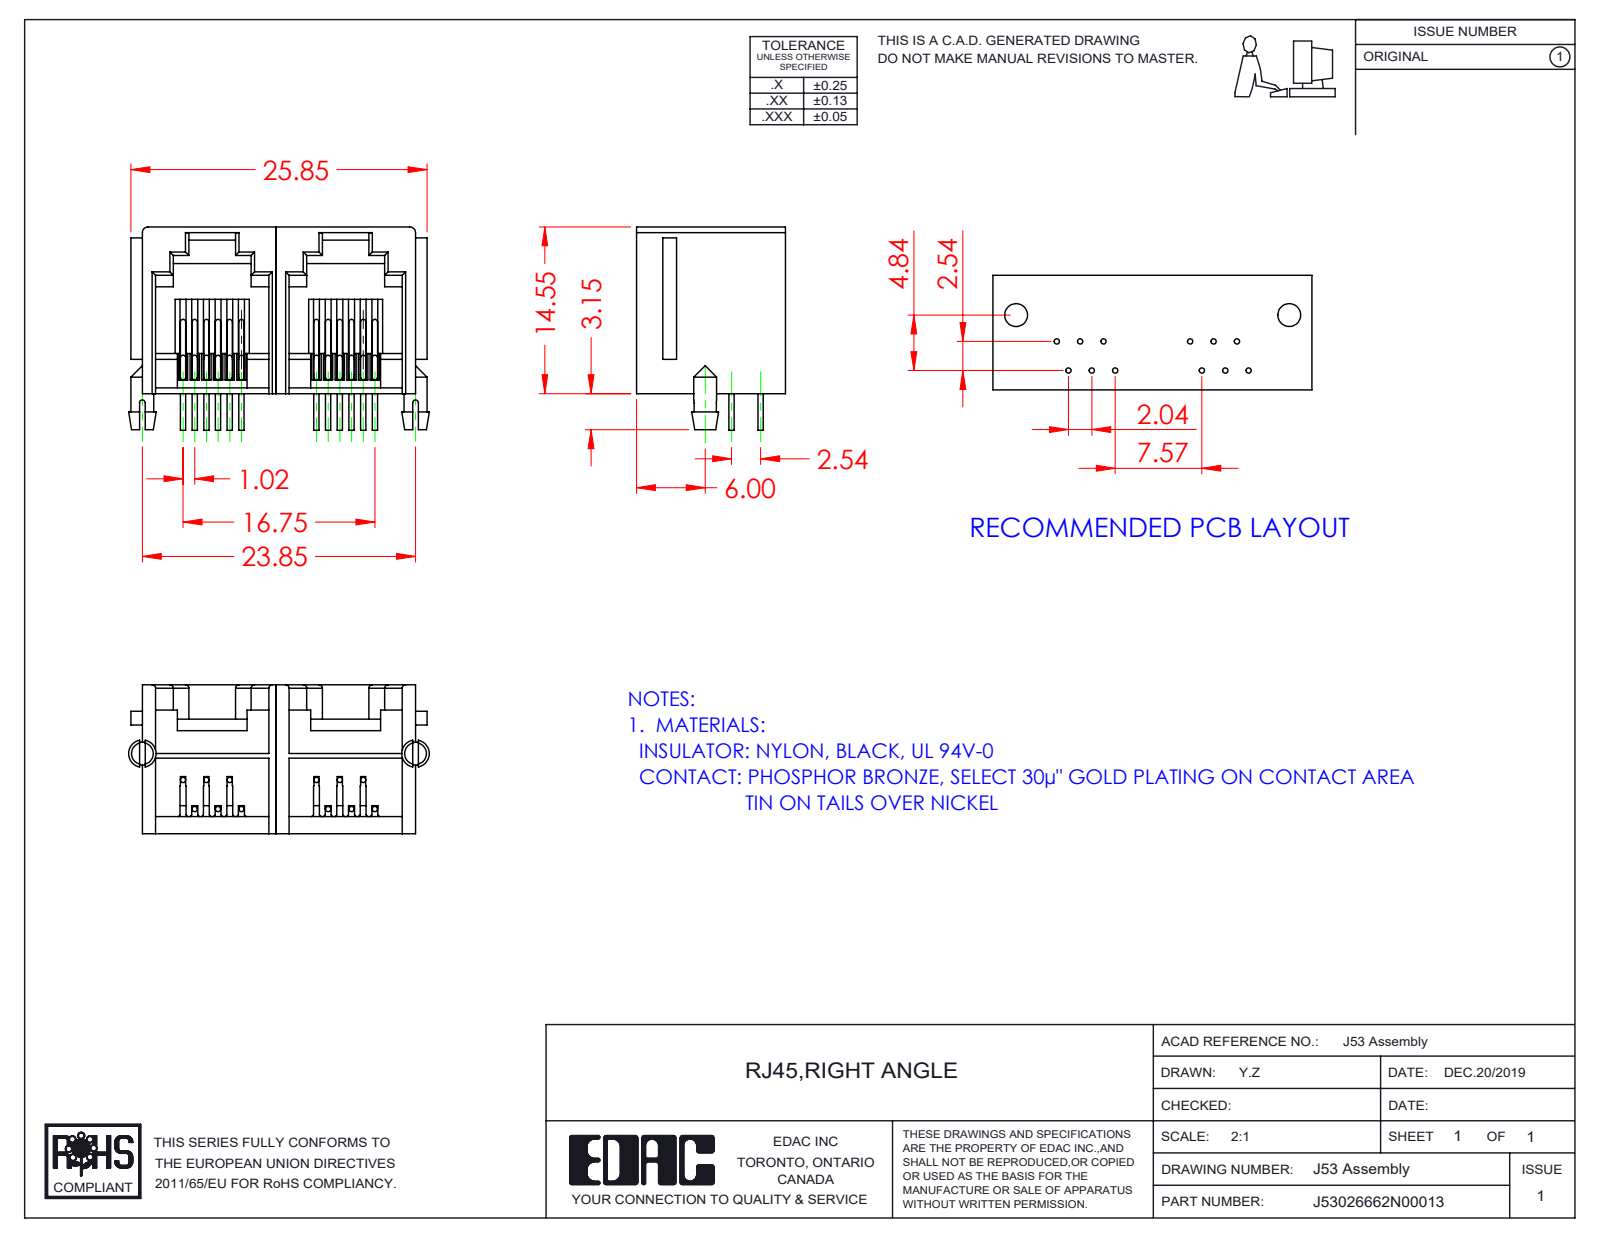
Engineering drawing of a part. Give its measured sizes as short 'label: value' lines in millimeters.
name: 53 Contact - 6; 53 Insulator RH; 53 Contacts; 53 Contact - 2 (+6 more)
written by: SolidWorks 2016 (CONFIG_CONTROL_DESIGN)
unit: mm
bodies: 14 solids, 595 faces (410 planar, 128 cylindrical, 57 other)
size: 26.25 × 17.75 × 13
volume: 1 800 mm³; area: 4 280 mm²
bosses: 36× ⌀0.46, 2× ⌀2
rounds: 14× R0.3, 10× R0.5, 2× R0.25, 1× R0.67
face distances: 11.65, 1.16, 11.04, 12.2, 22.69, 10.49, 12.81, 0.61, 9.88, 3
